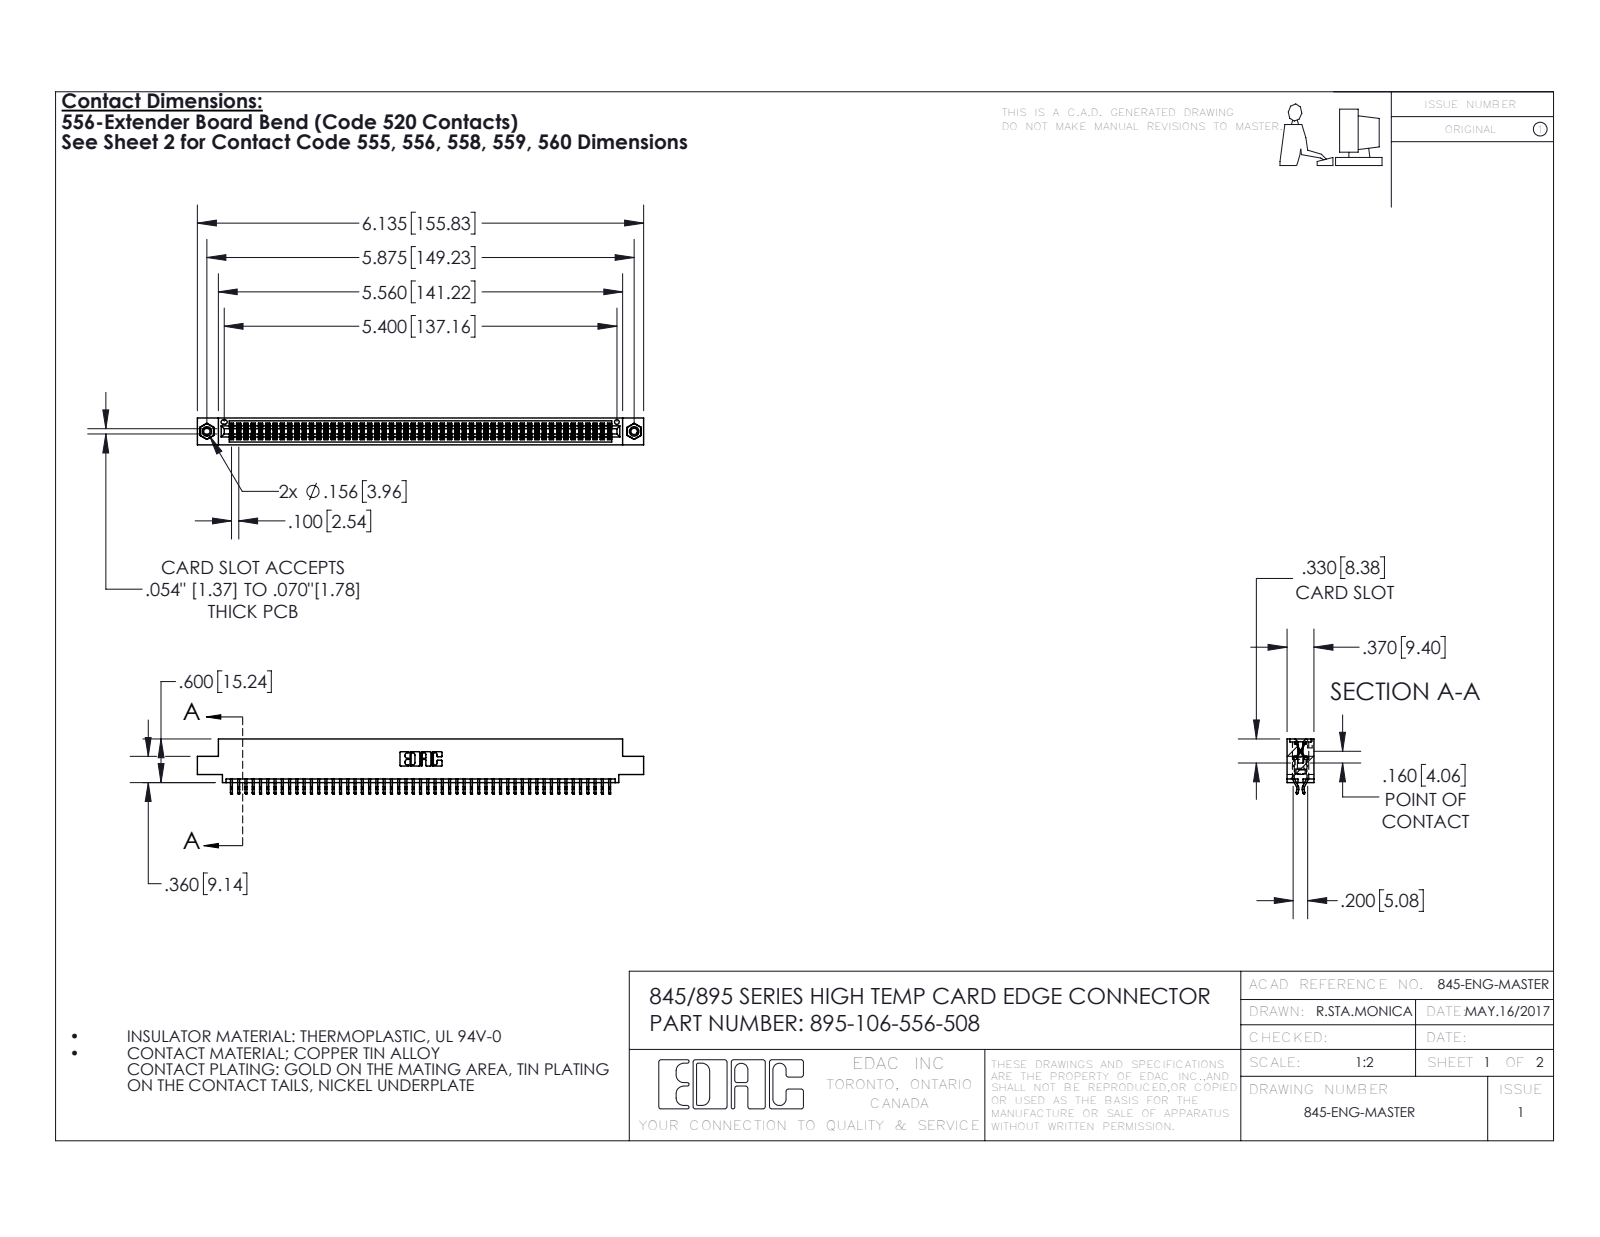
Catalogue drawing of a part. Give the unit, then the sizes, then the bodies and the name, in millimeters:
Units: millimetres
Overall size (bounding box): 155.8 × 19.2 × 9.4
Round holes (diameter × count): ⌀2.3 ×2, ⌀3.2 ×2, ⌀4 ×2, ⌀1.6 ×1
Round bosses / shafts (diameter × count): ⌀3.9 ×2
Partial cylindrical surfaces — rounded edges, fillets, slot ends (radius × count): R0.2 ×159, R0.3 ×22, R0.2 ×6, R0.8 ×6, R0.7 ×3, R0.3 ×2, R0.4 ×2, R0.5 ×2
Main face-to-face distances: 1.8, 7.6, 9.4, 5.1, 0.6, 2.5, 6.9, 5.7, 4.4, 3.8
Hole centre spacings: 6.9, 143.2, 149.2
Volume: 15 200 mm³ · Surface area: 22 630 mm²
Bodies: 109 solids, 6126 faces (4038 planar, 2072 cylindrical, 16 other)
Part name (STEP PRODUCT): 345-250-001_345-250-003-102; 345 Part_0.110 Offset - 0.156 Dia-TI; 345-292-001_556 Tail; 395-106-556-508
STEP written by: SolidWorks 2016 (CONFIG_CONTROL_DESIGN)
